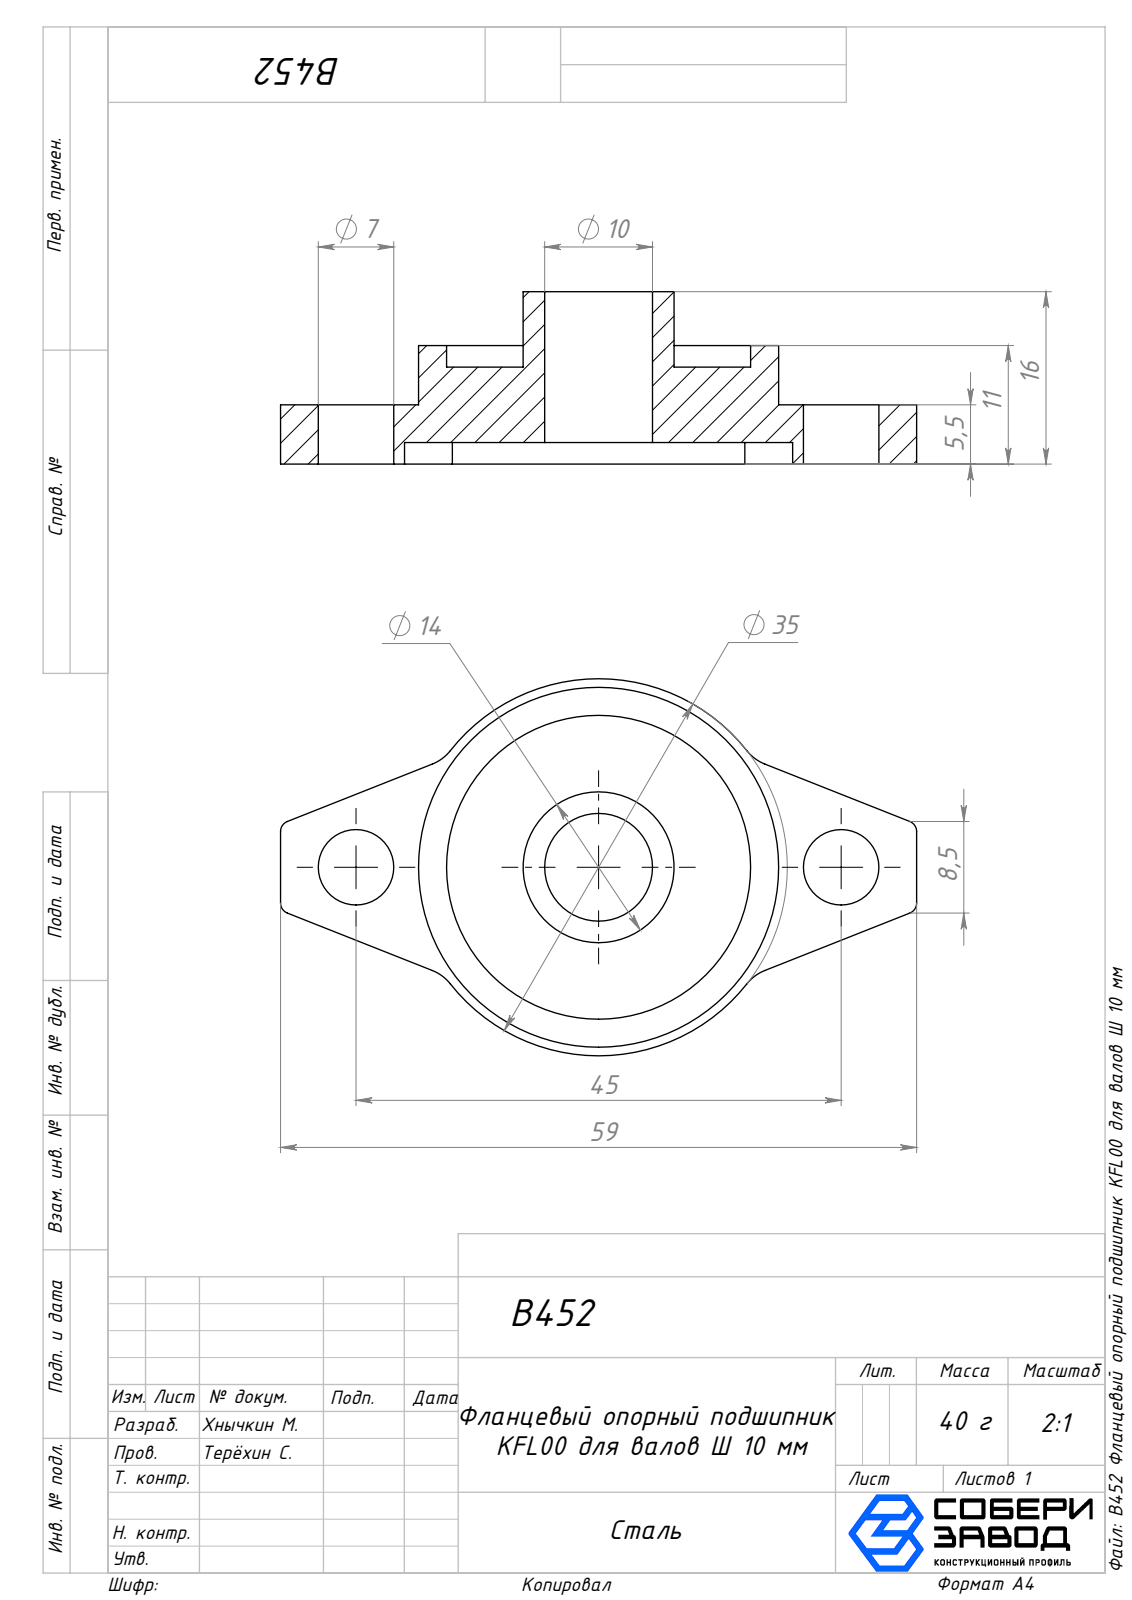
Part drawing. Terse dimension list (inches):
name: B452 Фланцевый опорный подшипник KFL00 для валов Ø 10 мм
written by: SolidWorks 2025 (AUTOMOTIVE_DESIGN)
unit: in
bodies: 1 solid, 44 faces (18 planar, 26 cylindrical, 0 other)
size: 2.323 × 1.378 × 0.63
volume: 0.525 in³; area: 7.852 in²
holes: 2× ⌀0.276, 1× ⌀0.394, 1× ⌀1.11
bosses: 1× ⌀1.315, 1× ⌀0.551
rounds: 4× R0.039, 4× R0.157, 1× R0.61, 1× R0.689
face distances: 0.138, 0.079, 0.354, 0.217, 0.276, 0.433, 1.149, 0.63, 0.551, 0.413
hole spacings: 0.886, 1.772
